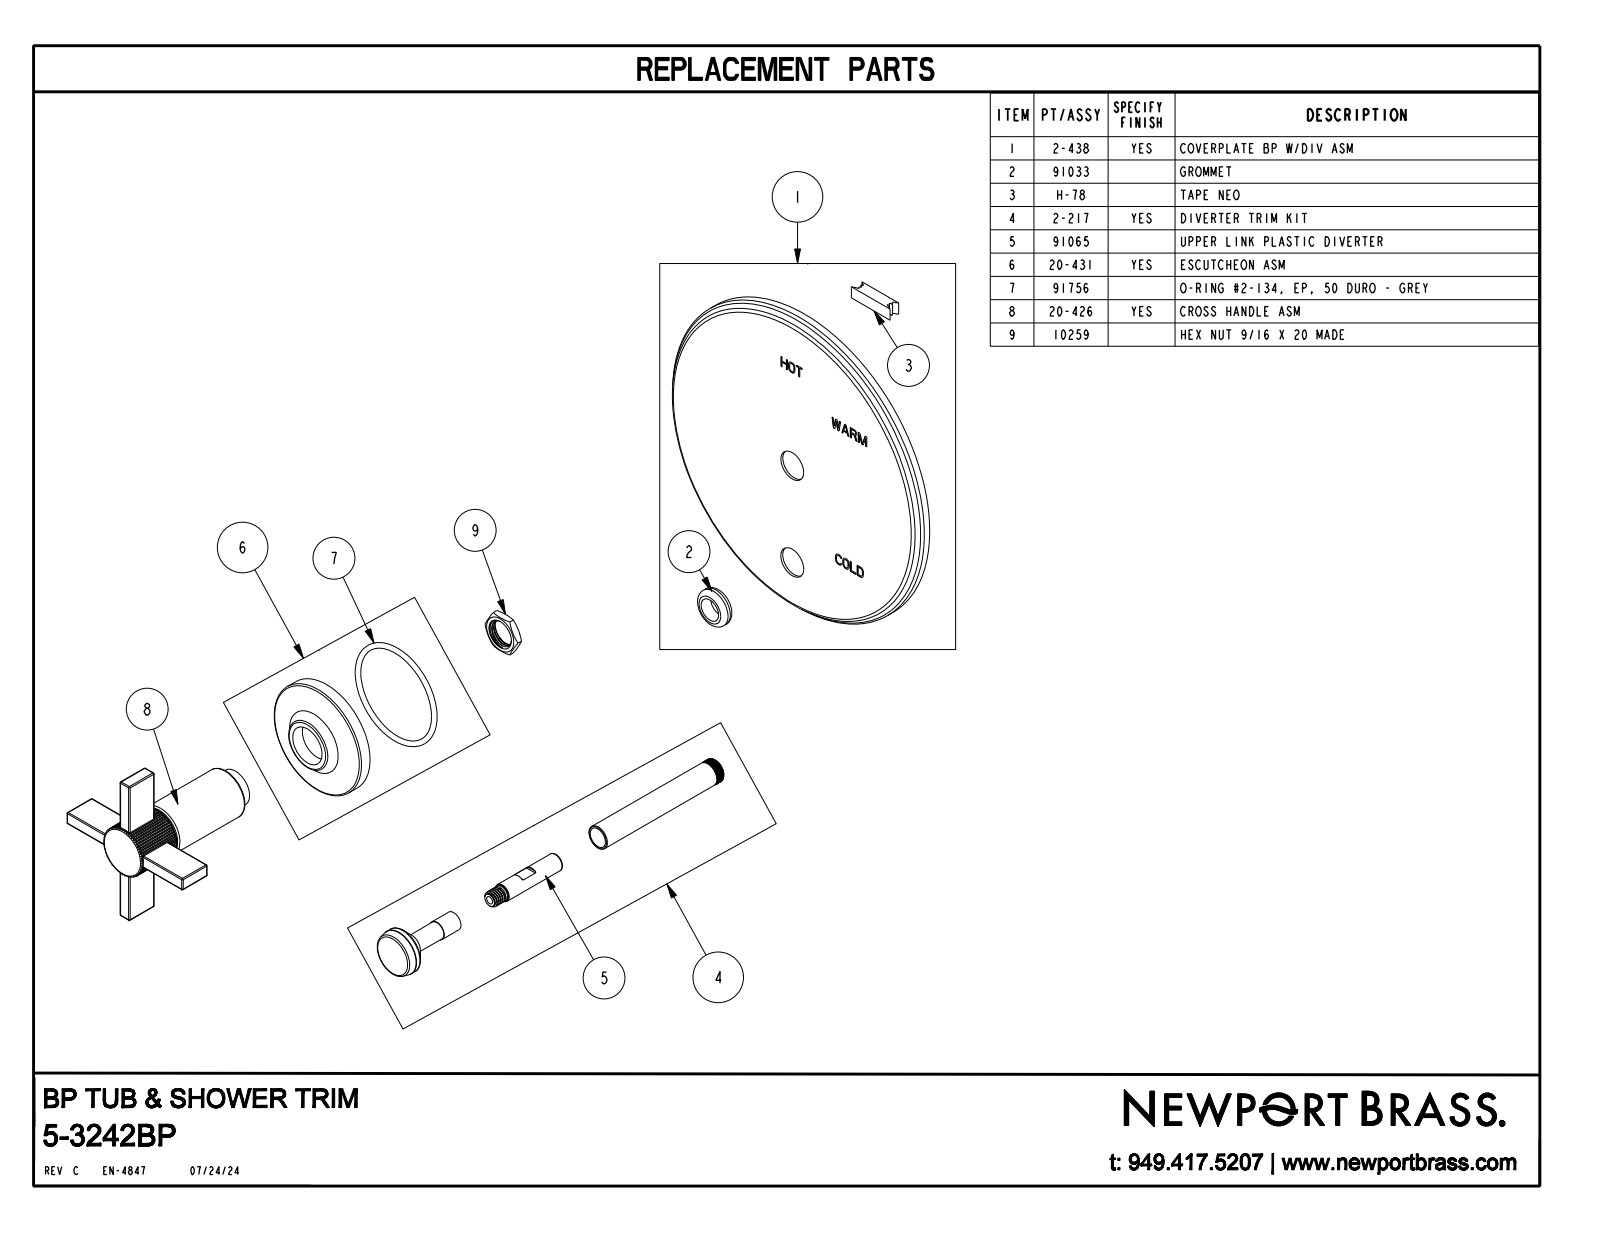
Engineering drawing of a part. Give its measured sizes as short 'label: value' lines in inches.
name: 11118_AF0; 91033; H-78; 2-438_AF0_ASM (+8 more)
written by: CREO PARAMETRIC BY PTC INC, 2018400 (CONFIG_CONTROL_DESIGN)
unit: in
bodies: 26 solids, 2681 faces (1076 planar, 1014 cylindrical, 591 other)
size: 6.5 × 6.5 × 6.051
volume: 5.509 in³; area: 211 in²
holes: 5× ⌀0.11, 5× ⌀0.15, 1× ⌀0.14, 1× ⌀0.265, 1× ⌀0.275, 1× ⌀0.318, 1× ⌀0.335, 1× ⌀0.345, 1× ⌀0.358, 1× ⌀0.375, 1× ⌀0.383, 1× ⌀0.397
bosses: 5× ⌀0.138, 1× ⌀6.5, 1× ⌀2.25, 1× ⌀1.812, 1× ⌀1, 1× ⌀0.9, 1× ⌀0.85, 1× ⌀0.73
rounds: 40× R0.02, 12× R0.1, 8× R0.03, 8× R0.094, 6× R0.01, 6× R0.042, 1× R0.072, 1× R0.137
face distances: 0.05, 0.25, 0.225, 2.321, 0.3, 2.546, 3.196, 2.496, 3.146, 0.65
hole spacings: 0.335, 0.474, 0.67, 2.196, 1.835, 2.17, 2.505
